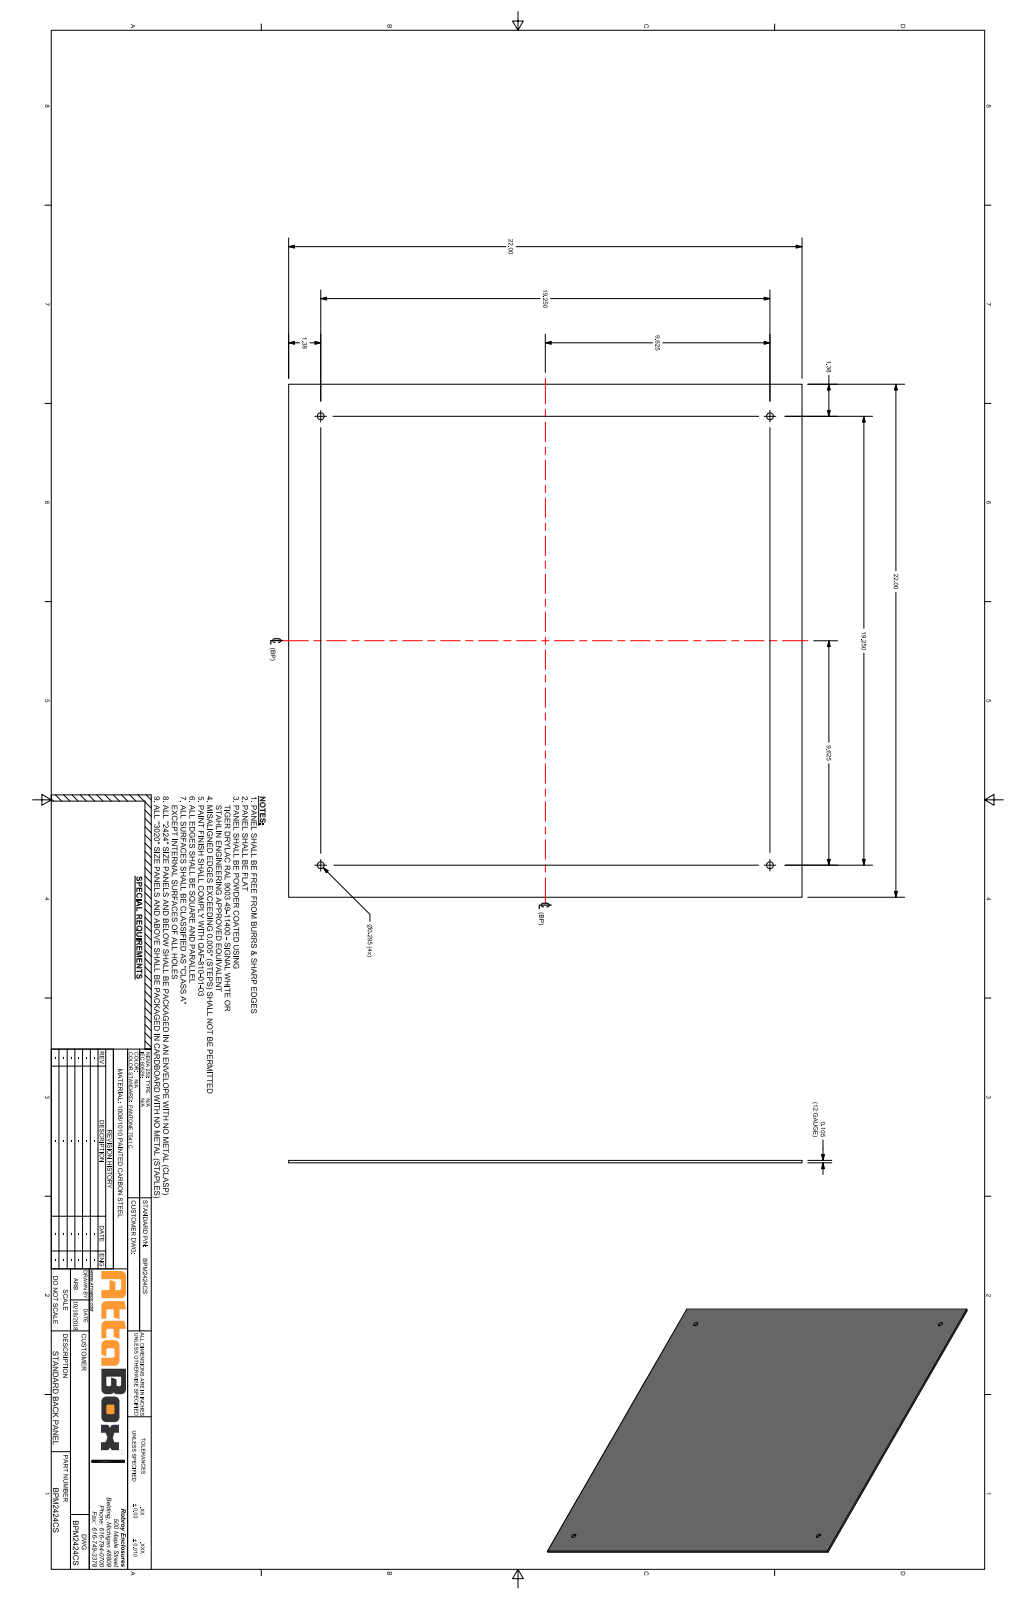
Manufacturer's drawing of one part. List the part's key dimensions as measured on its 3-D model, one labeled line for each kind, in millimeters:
Part name (STEP PRODUCT): HW-MP2424CS
STEP written by: Autodesk Inventor 2017 (CONFIG_CONTROL_DESIGN)
Units: millimetres
Bodies: 1 solid, 10 faces (6 planar, 4 cylindrical, 0 other)
Overall size (bounding box): 558.8 × 558.8 × 2.67
Volume: 832 320 mm³ · Surface area: 630 375 mm²
Round holes (diameter × count): ⌀7.49 ×4
Main face-to-face distances: 2.67, 558.8
Hole centre spacings: 488.96, 691.49
